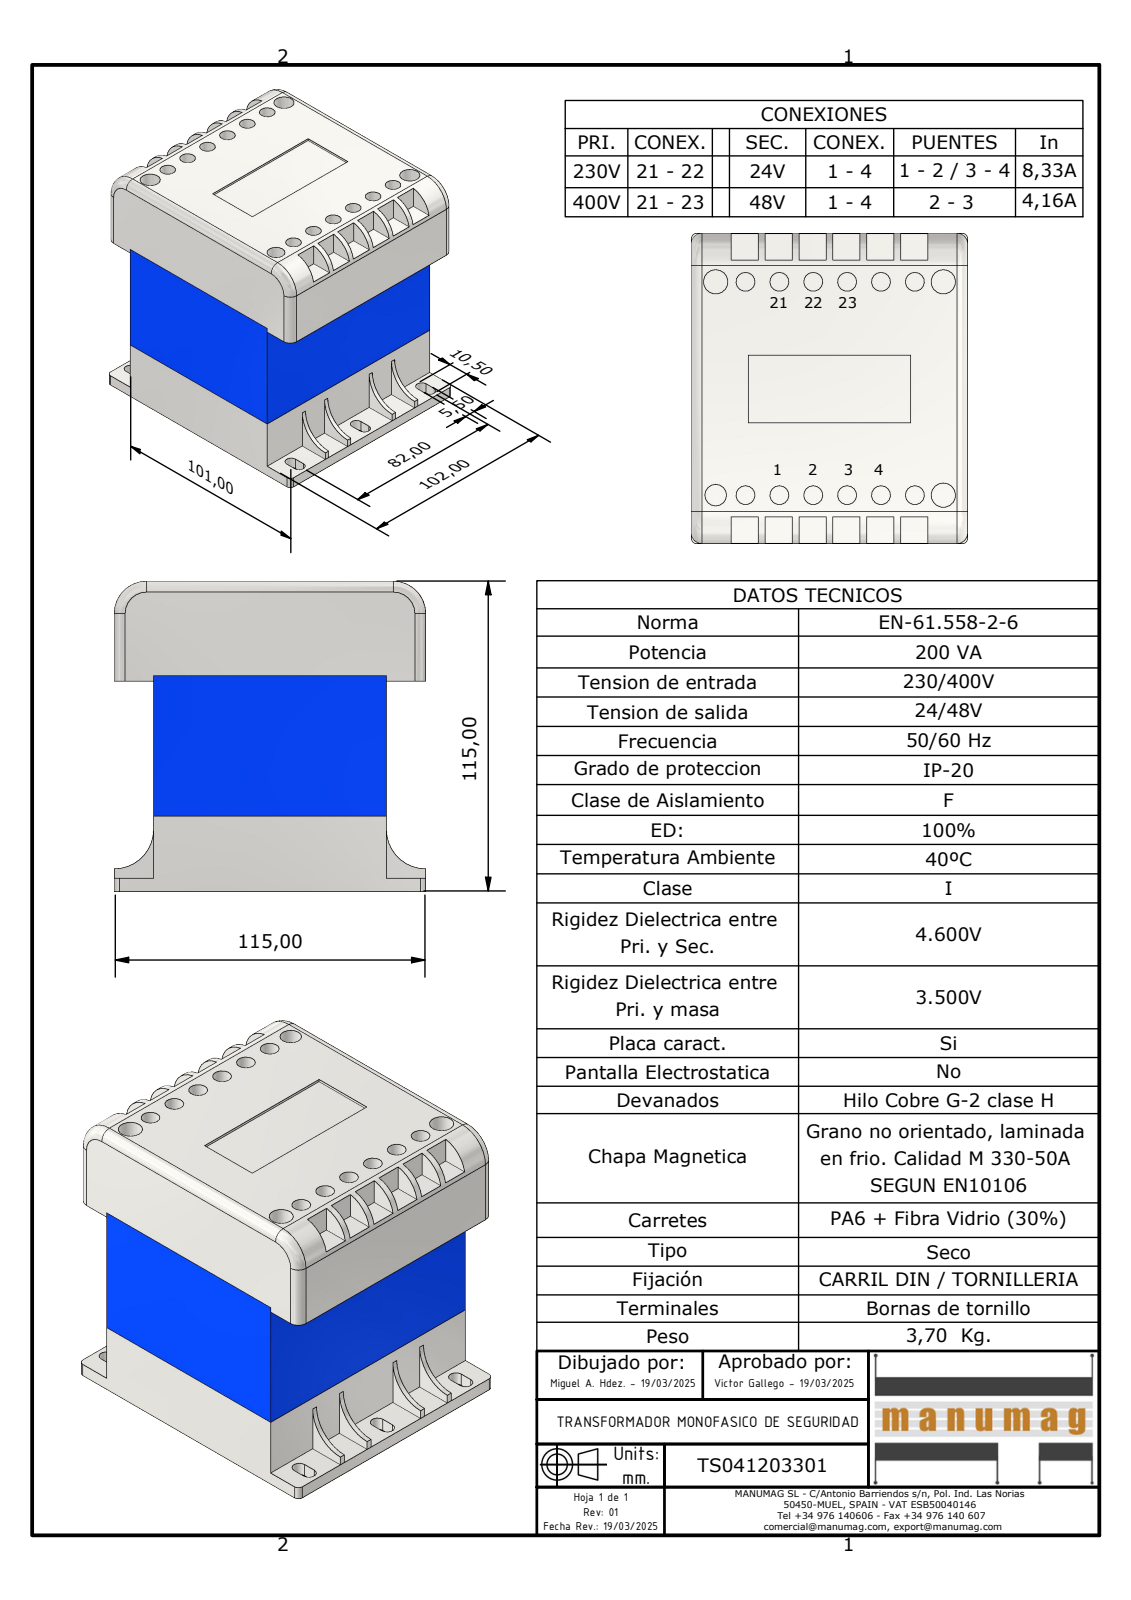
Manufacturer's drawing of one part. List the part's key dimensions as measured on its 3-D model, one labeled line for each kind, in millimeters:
Part name (STEP PRODUCT): TS041203301; INFERIOR EI96; CENTRAL EI96-50; SUPERIOR EI96
STEP written by: Autodesk Inventor 2023 (AUTOMOTIVE_DESIGN)
Units: millimetres
Bodies: 11 solids, 200 faces (152 planar, 44 cylindrical, 4 other)
Overall size (bounding box): 115 × 115 × 102
Volume: 479 280 mm³ · Surface area: 128 707 mm²
Round holes (diameter × count): ⌀7 ×12, ⌀9 ×3, ⌀8 ×1
Partial cylindrical surfaces — rounded edges, fillets, slot ends (radius × count): R2.5 ×8, R4 ×6, R2 ×4, R12 ×2, R14.5 ×2
Main face-to-face distances: 1, 85, 101, 5, 102, 80, 115, 75, 86, 100
Hole centre spacings: 12.5, 79.98, 25, 79, 82.86, 37.5, 87.45, 50
